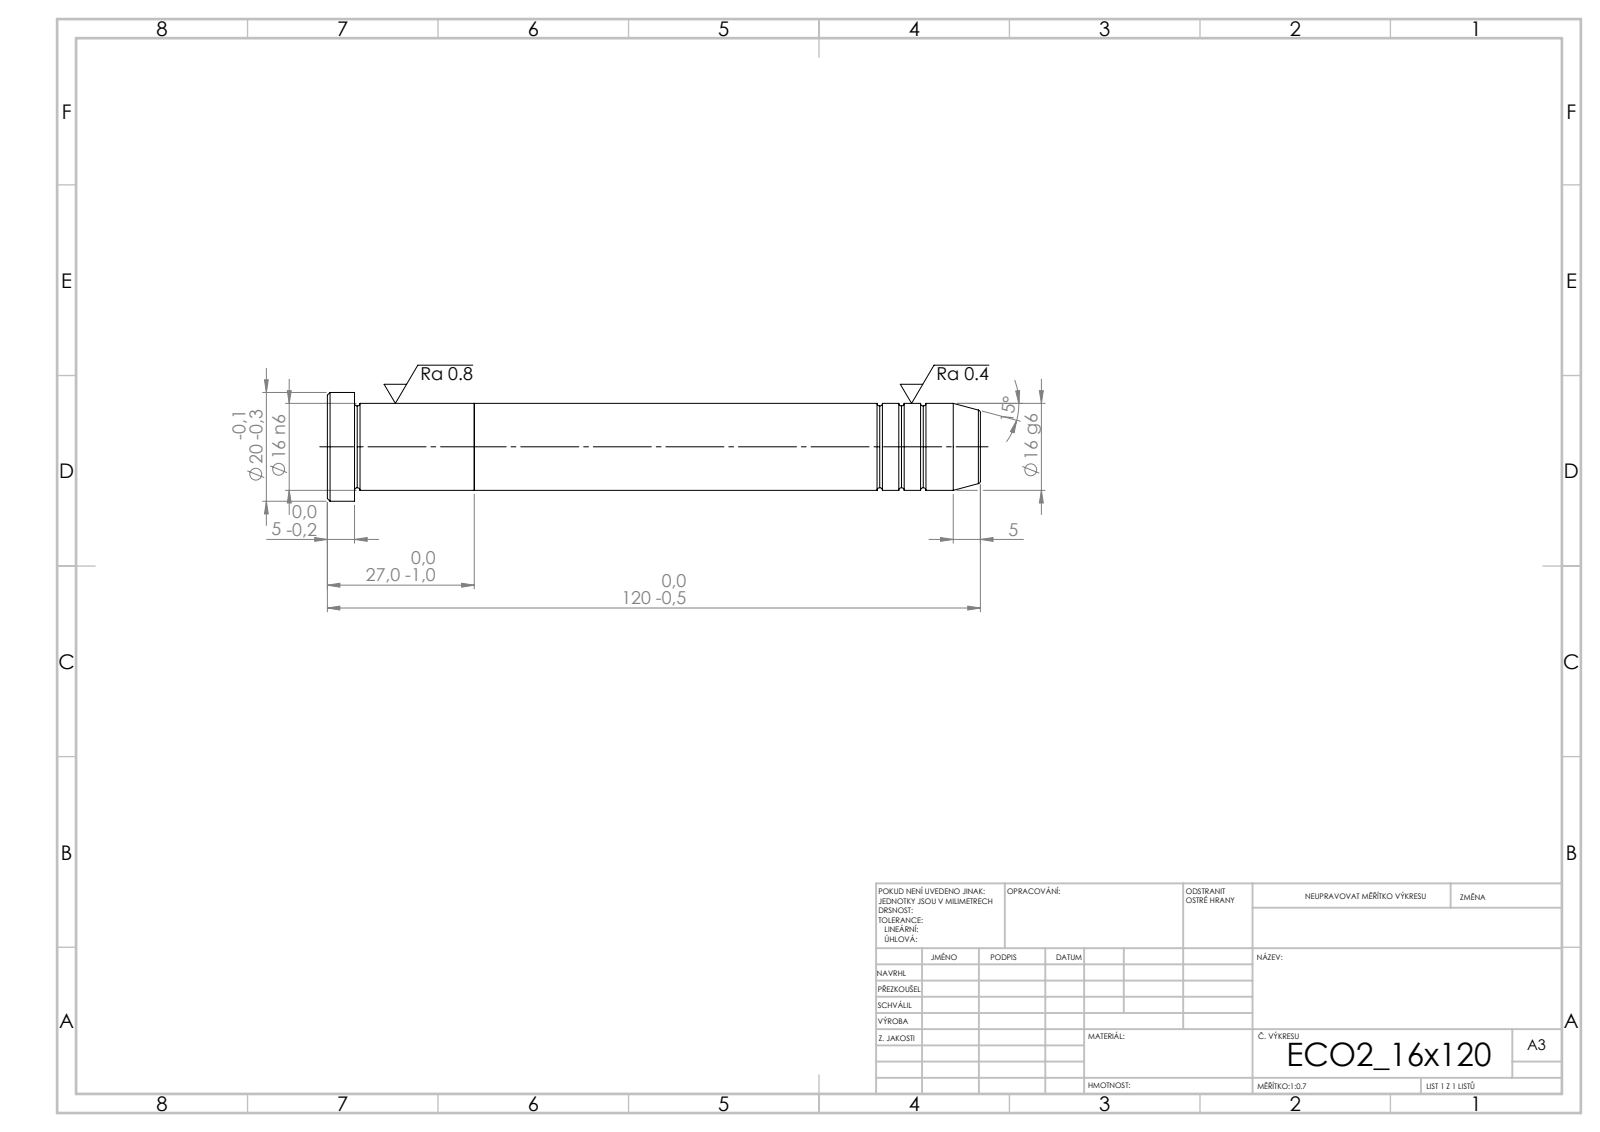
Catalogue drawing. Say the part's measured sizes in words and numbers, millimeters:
Its 3-D file was written by "SolidWorks 2019 (CONFIG_CONTROL_DESIGN)". It is 2 solids with 39 faces: 5 planar, 12 cylindrical and 22 other. Overall it measures 120 by 20 by 20 millimeters. Its volume is 24 448 cubic millimeters and its surface area 7 129 square millimeters. Round bosses or shafts: 1 of diameter 20, 1 of diameter 16. The main face-to-face distances are 27, 93, 120, 115, 22, 5.
